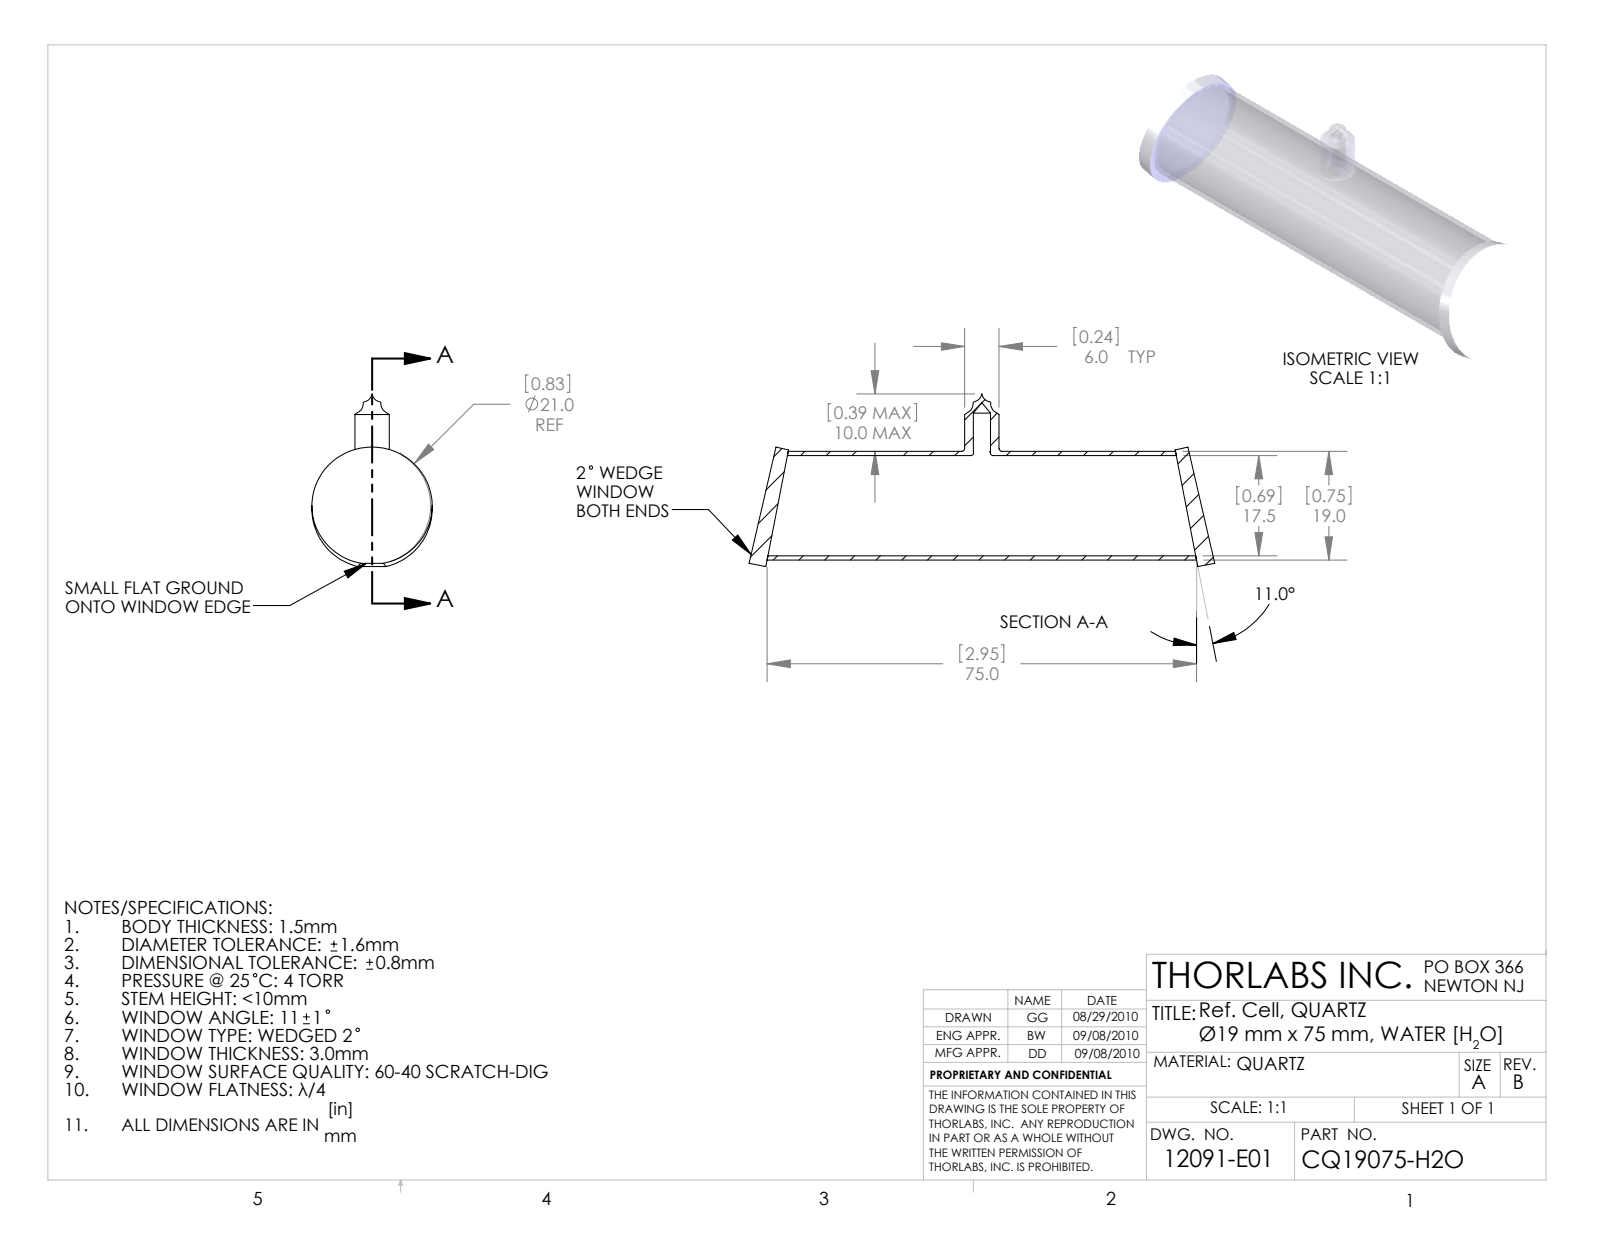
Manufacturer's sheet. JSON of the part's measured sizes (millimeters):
{"part_name": "12091-E0W", "step_written_by": "SolidWorks 2009 (AUTOMOTIVE_DESIGN)", "units": "millimeters", "bodies": {"solids": 3, "faces": 33, "planar": 8, "cylindrical": 17, "other": 8}, "overall_size": [81.31, 30.12, 21], "volume_mm3": 5042, "surface_area_mm2": 10206, "round_holes": [[2.91, 1], [3, 1], [17.5, 1]], "round_bosses_or_shafts": [[21, 2], [19, 1], [6, 1]]}
